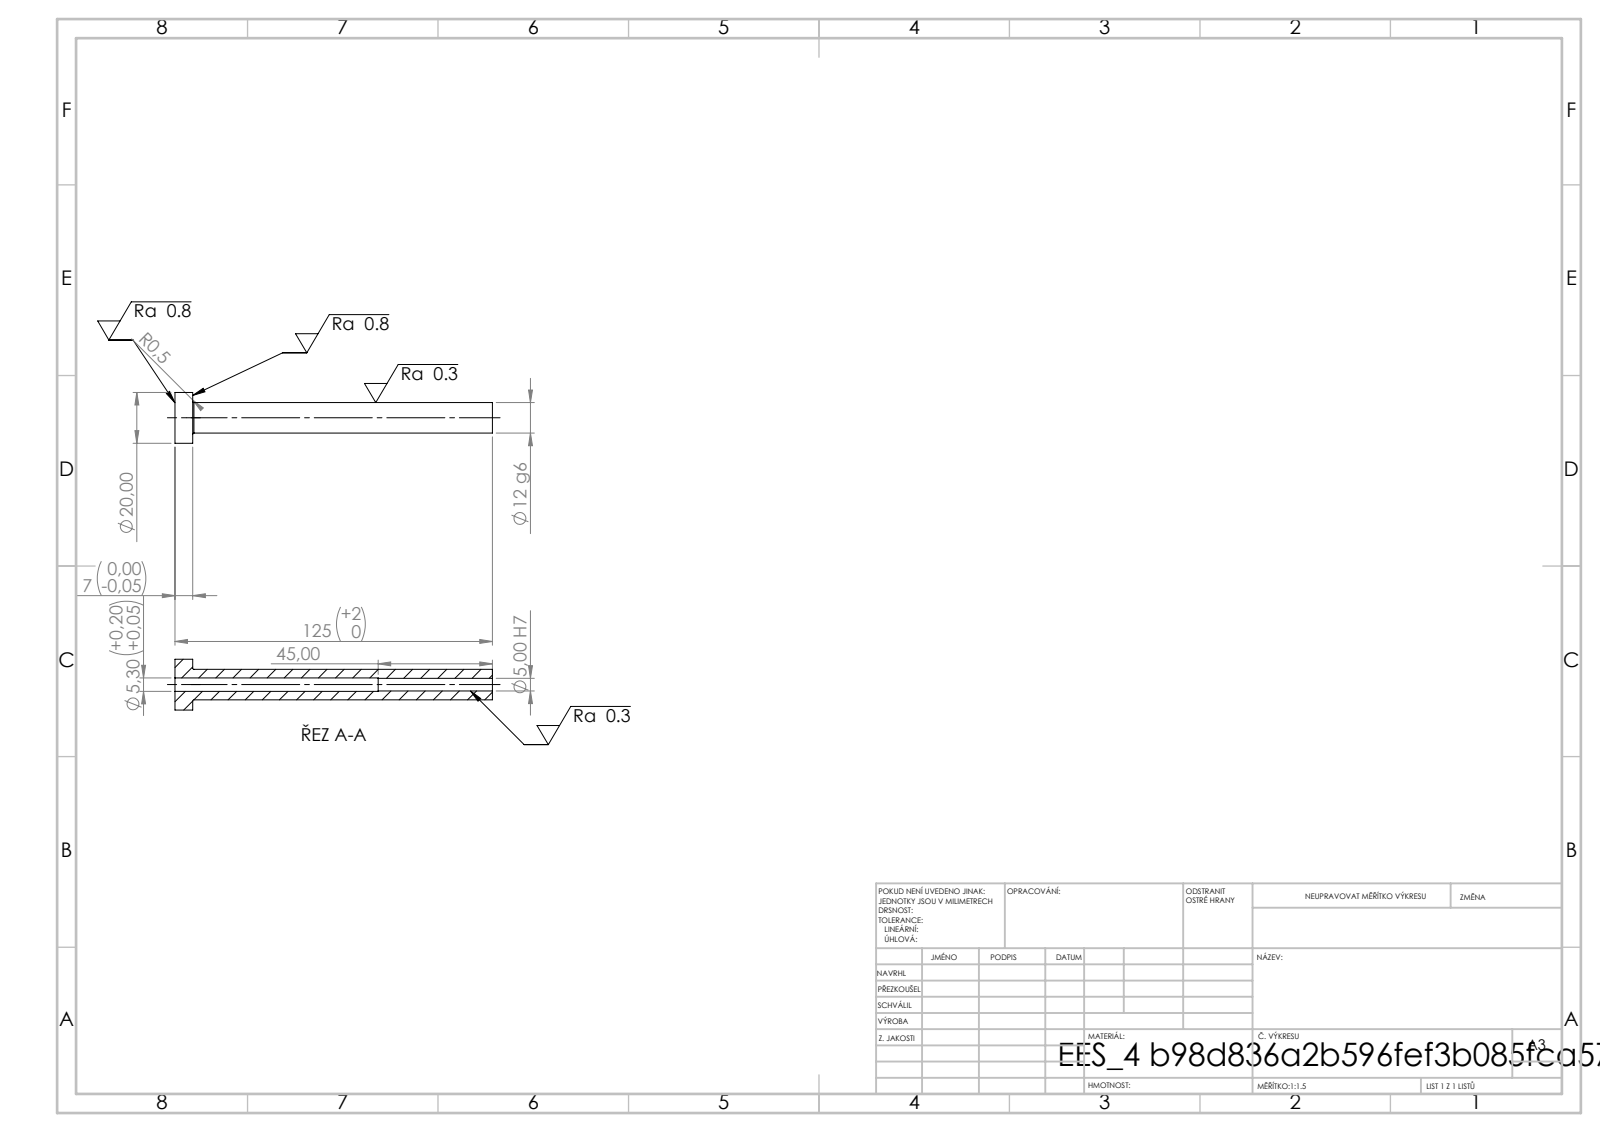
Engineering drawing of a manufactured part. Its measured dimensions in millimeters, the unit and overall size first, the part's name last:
Units: millimetres
Overall size (bounding box): 125 × 20 × 20
Round holes (diameter × count): ⌀5 ×1, ⌀5.3 ×1
Round bosses / shafts (diameter × count): ⌀20 ×1, ⌀12 ×1
Main face-to-face distances: 7, 125, 118, 80, 73, 45
Volume: 12 898 mm³ · Surface area: 7 508 mm²
Bodies: 1 solid, 14 faces (4 planar, 8 cylindrical, 2 other)
STEP written by: SolidWorks 2019 (CONFIG_CONTROL_DESIGN)
